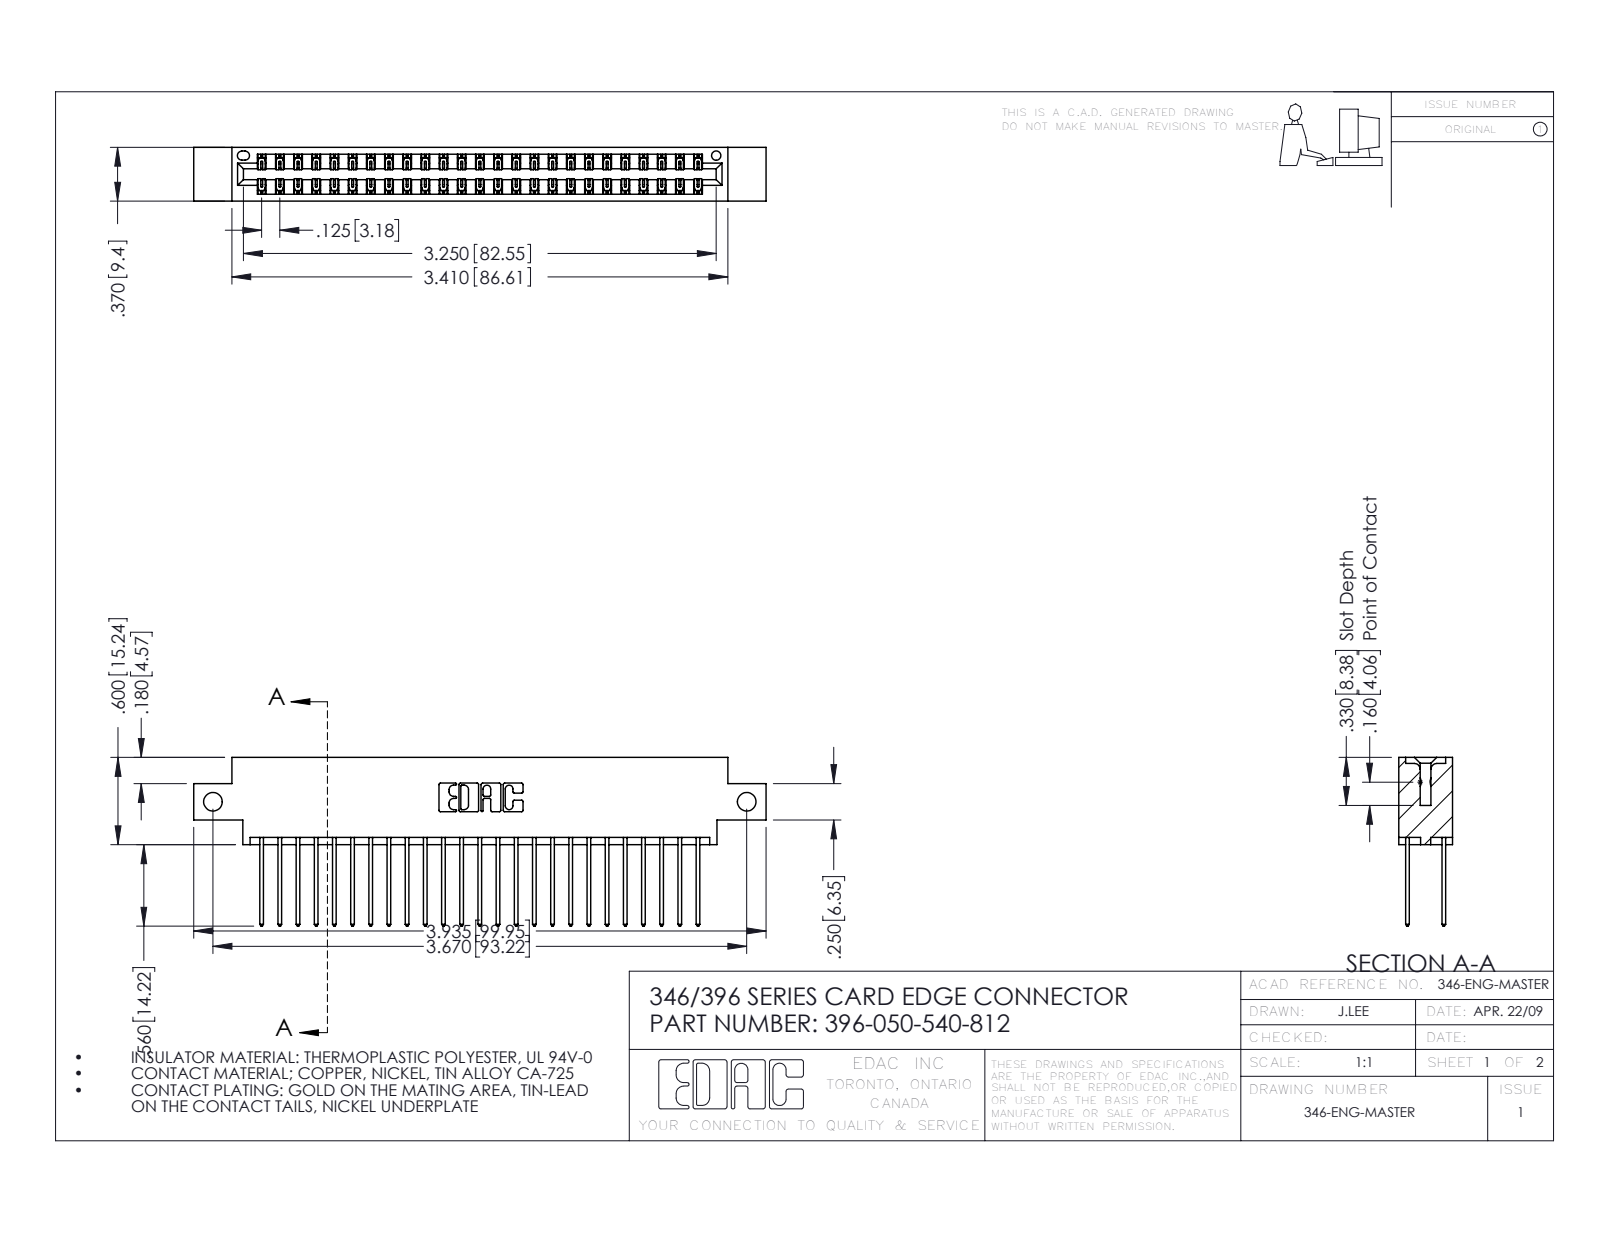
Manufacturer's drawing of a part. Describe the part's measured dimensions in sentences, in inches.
The part is named "346 Part_0.170 Offset - Side Mount; 345-292-001_345-293-140; 396-050-540-812". Its 3-D file was written by "SolidWorks 2016 (CONFIG_CONTROL_DESIGN)". It is 51 solids with 2726 faces: 1830 planar, 896 cylindrical and 0 other. Overall it measures 3.935 by 1.16 by 0.37 inches. Its volume is 0.584 cubic inches and its surface area 21.41 square inches. Round holes: 2 of diameter 0.128, 1 of diameter 0.064. Partial cylindrical surfaces (rounded edges, fillets, slot ends): 75 of radius 0.006, 50 of radius 0.01, 22 of radius 0.01, 6 of radius 0.007, 6 of radius 0.031, 3 of radius 0.026, 2 of radius 0.014, 2 of radius 0.022. The main face-to-face distances are 0.048, 0.322, 0.25, 0.37, 0.072, 0.298, 0.025, 0.275, 0.148, 0.222. The hole center spacings are 3.67.
